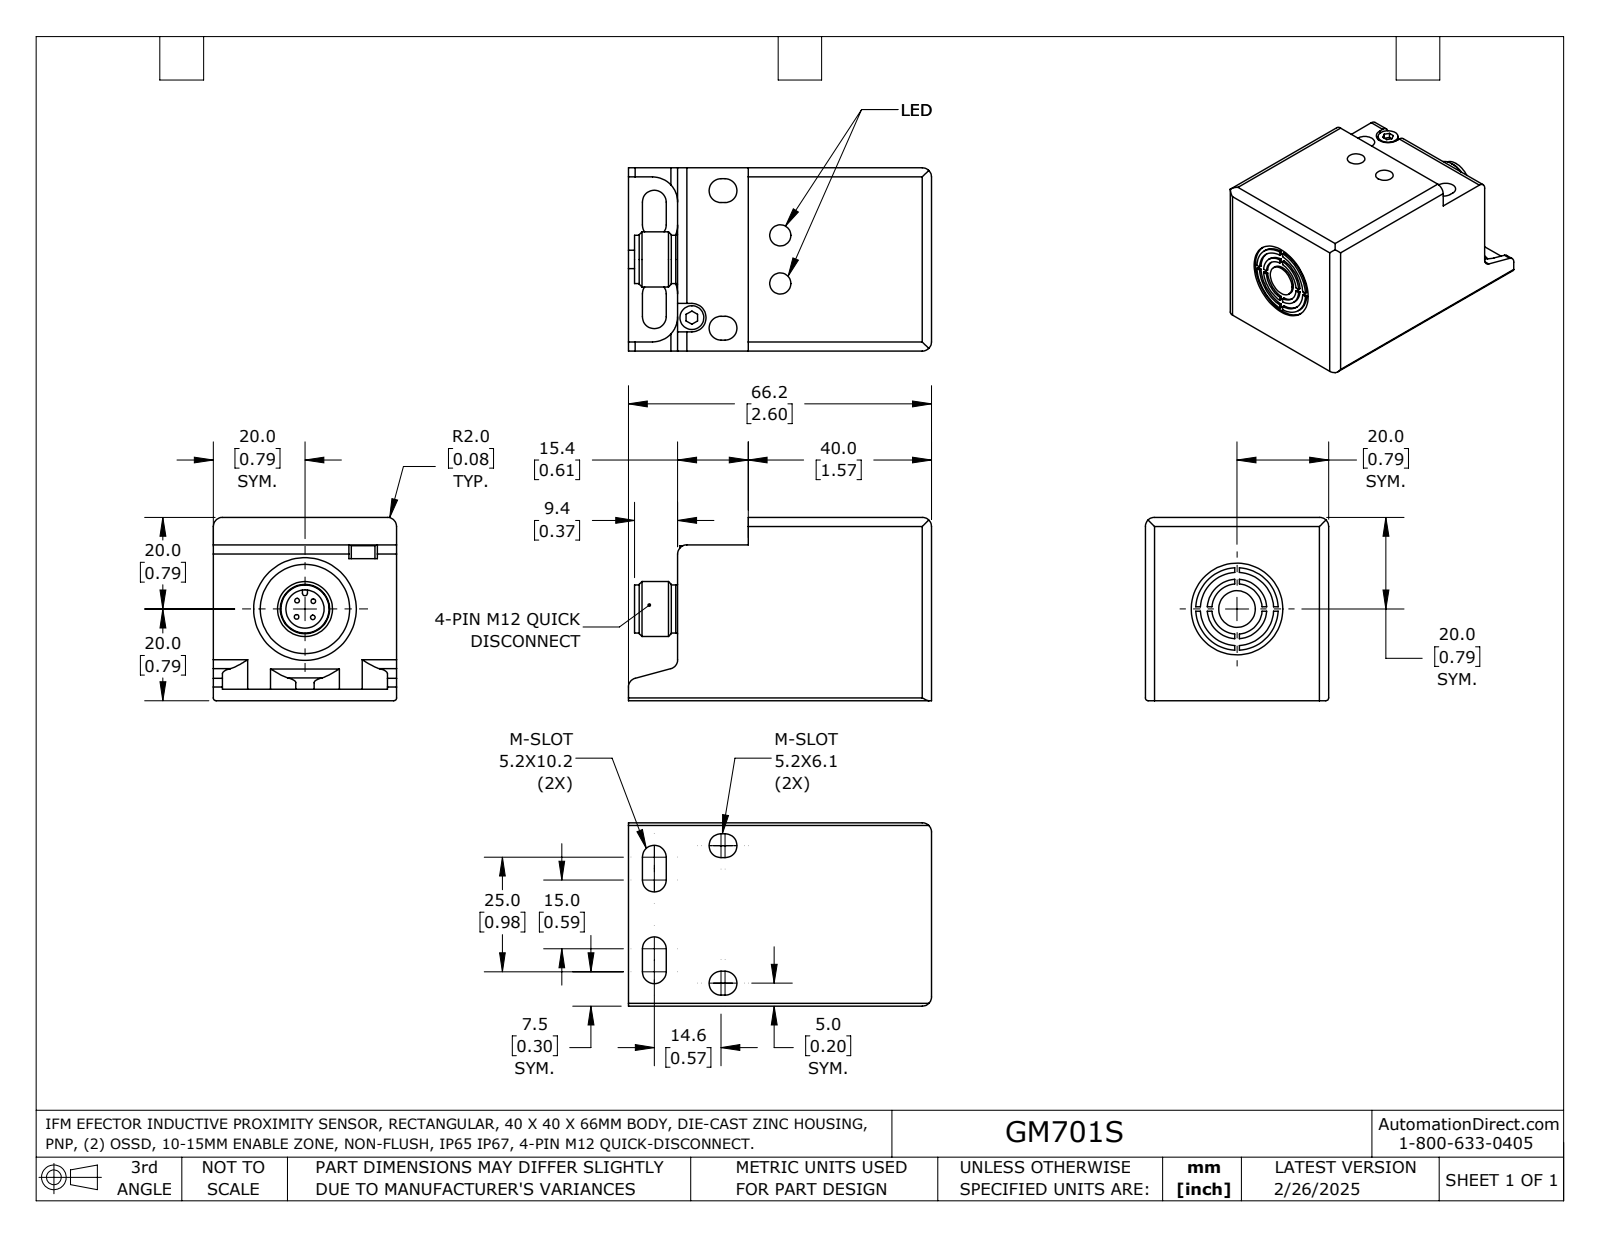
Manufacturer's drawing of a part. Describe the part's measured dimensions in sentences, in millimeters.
The part is named "GM701S". Its 3-D file was written by "SolidWorks 2024 (AUTOMOTIVE_DESIGN)". It is 1 solid with 132 faces: 74 planar, 55 cylindrical and 3 other. Overall it measures 66.15 by 40 by 40 millimeters. Its volume is 84 277 cubic millimeters and its surface area 14 729 square millimeters. Round holes: 2 of diameter 4.6, 1 of diameter 8.35, 1 of diameter 11, 1 of diameter 16, 1 of diameter 19.5, 1 of diameter 20, 1 of diameter 22.4. Round bosses or shafts: 1 of diameter 18, 1 of diameter 13, 1 of diameter 12, 1 of diameter 10.5, 1 of diameter 8, 1 of diameter 5.2. Partial cylindrical surfaces (rounded edges, fillets, slot ends): 9 of radius 2, 8 of radius 2.6, 4 of radius 5.5, 2 of radius 0.6, 1 of radius 0.55, 1 of radius 3.1. The main face-to-face distances are 40, 55.4, 34, 6, 2.5, 15.4, 0.5, 31.5, 37.5, 15.2. The hole center spacings are 10.5.
